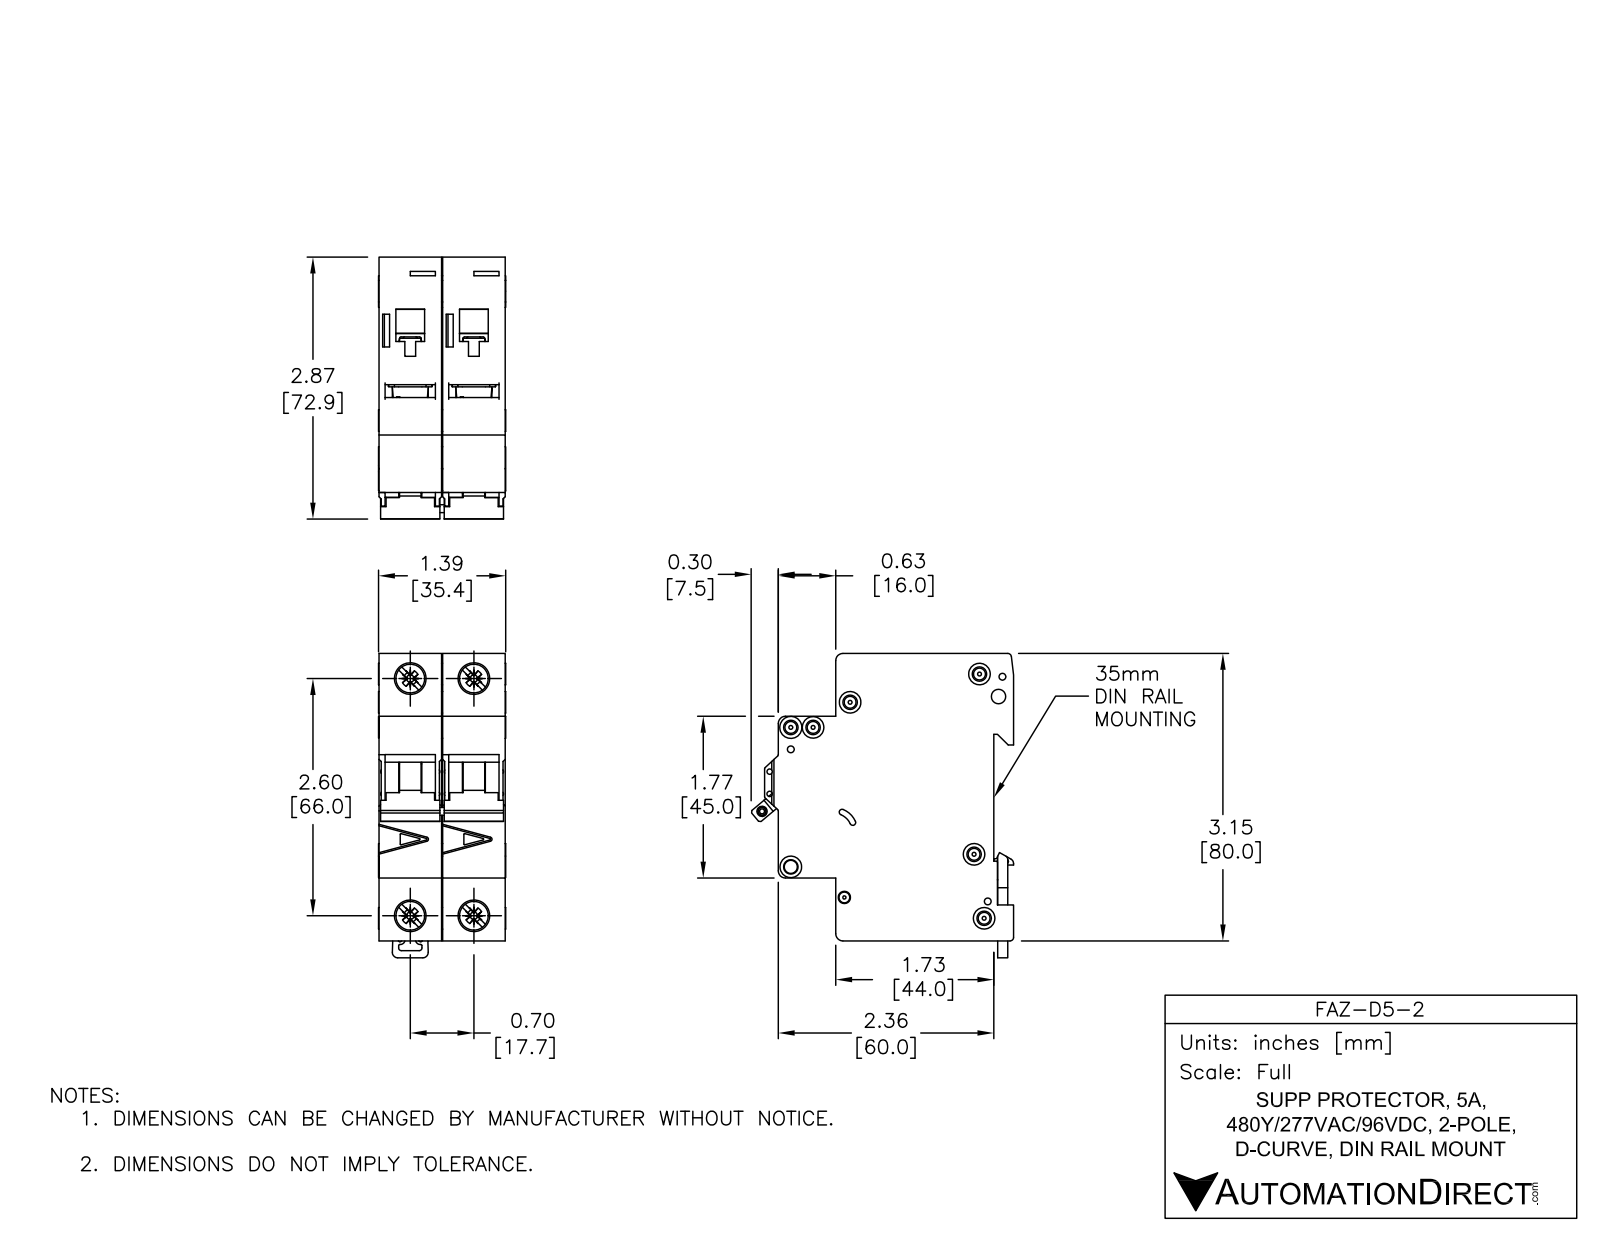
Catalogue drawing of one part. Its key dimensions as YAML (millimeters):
part_name: "FAZ-D5-2"
step_written_by: "SolidWorks 2014 (AUTOMOTIVE_DESIGN)"
units: millimeters
bodies: {solids: 8, faces: 1104, planar: 466, cylindrical: 396, other: 242}
overall_size: [84.78, 73.04, 35.4]
volume: 149808
surface_area: 38799
round_holes:
  - {diameter: 3.6, count: 6}
  - {diameter: 1.9, count: 3}
  - {diameter: 1.09, count: 2}
  - {diameter: 1.5, count: 2}
  - {diameter: 4, count: 2}
  - {diameter: 7.15, count: 2}
  - {diameter: 8.2, count: 2}
  - {diameter: 2.15, count: 1}
  - {diameter: 2.2, count: 1}
  - {diameter: 2.55, count: 1}
  - {diameter: 3.3, count: 1}
  - {diameter: 3.4, count: 1}
round_bosses_or_shafts:
  - {diameter: 6, count: 4}
  - {diameter: 8.2, count: 2}
  - {diameter: 2.5, count: 2}
partial_cylinders:
  - {radius: 0.25, count: 49}
  - {radius: 0.5, count: 19}
  - {radius: 2, count: 10}
  - {radius: 0.2, count: 8}
  - {radius: 1, count: 8}
  - {radius: 0.8, count: 2}
  - {radius: 1.8, count: 2}
  - {radius: 3, count: 2}
face_to_face_distances: [17.7, 17.5, 35.2, 79.48, 5.5, 49.5, 44, 65.5, 60, 16]
hole_center_spacings: [6.2, 13.64, 17.7, 66, 68.33, 4.81, 5.19, 5.61]
